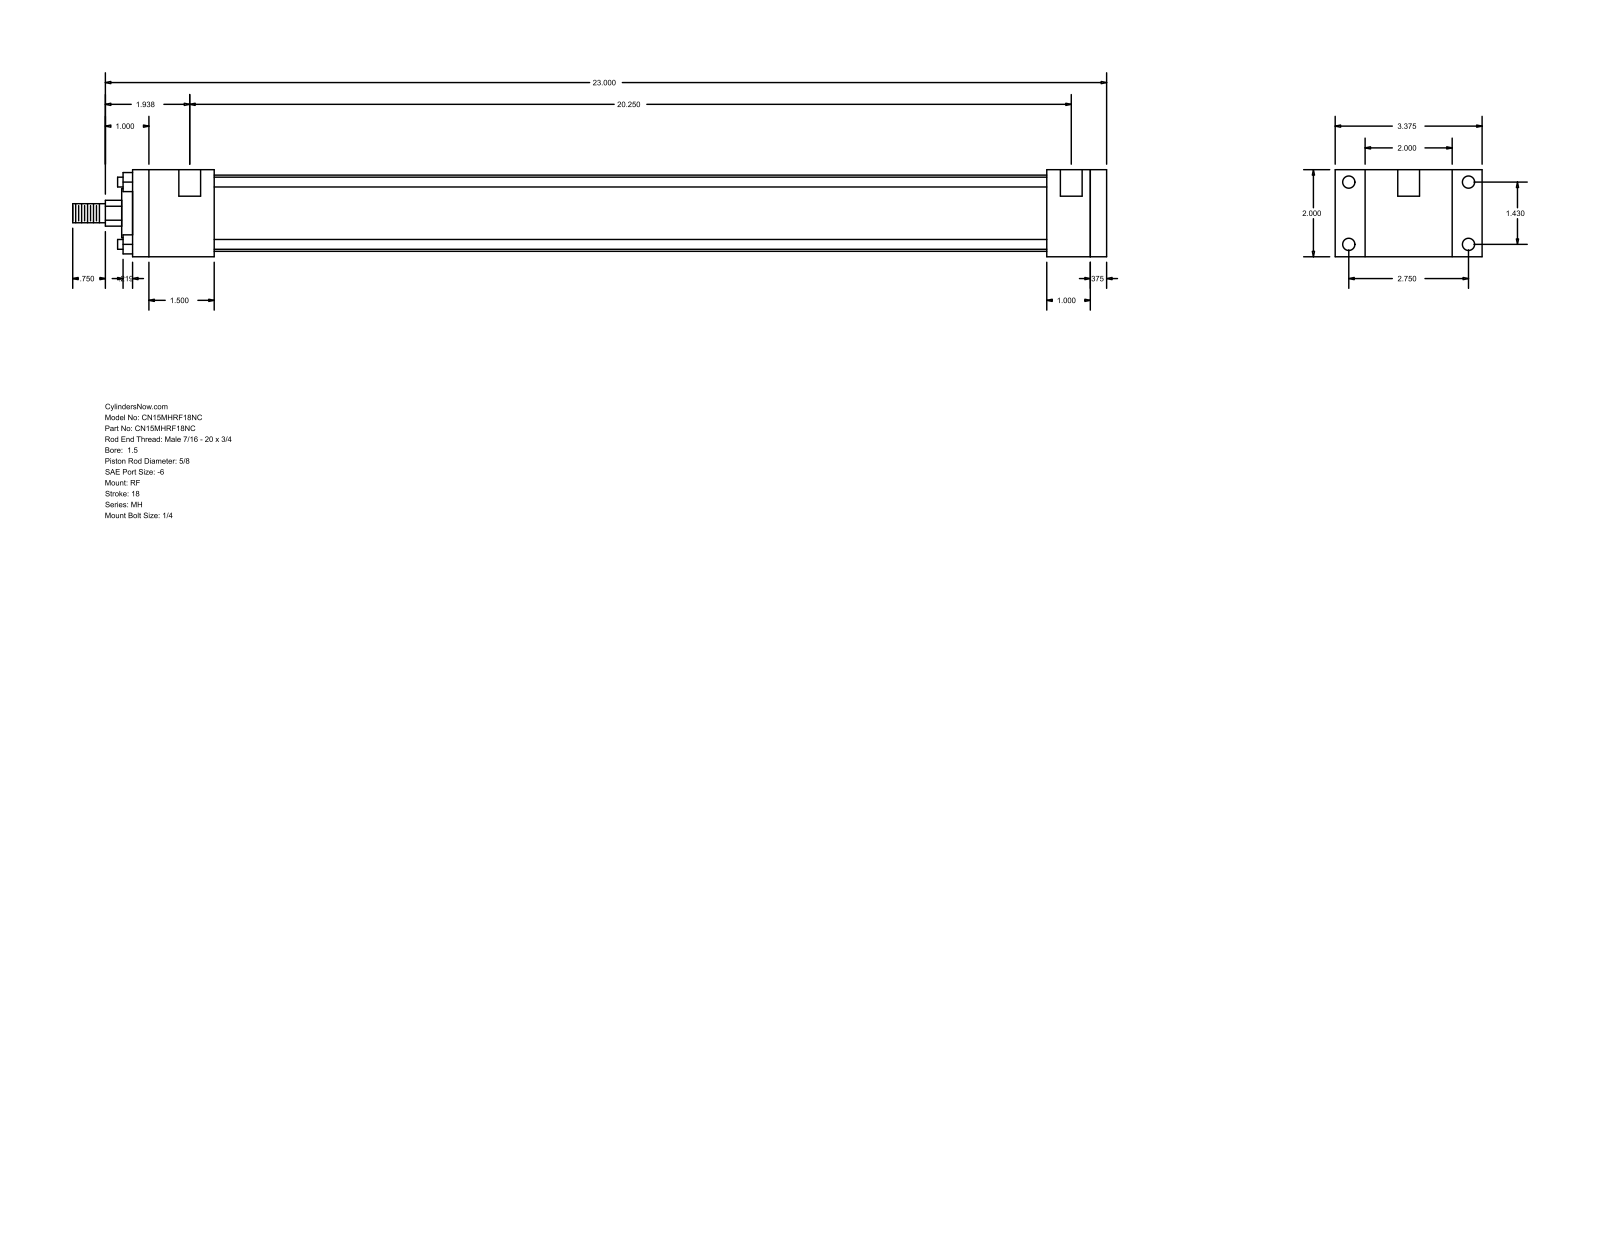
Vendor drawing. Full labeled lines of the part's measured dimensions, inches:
Part name (STEP PRODUCT): MH_RF__0150_0.625
STEP written by: GSSL Pune (CONFIG_CONTROL_DESIGN)
Units: inches
Bodies: 0 solids, 92 faces (64 planar, 28 cylindrical, 0 other)
Overall size (bounding box): 23.75 × 3.375 × 2
Round holes (diameter × count): ⌀0.219 ×4, ⌀0.281 ×4, ⌀0.5 ×2
Round bosses / shafts (diameter × count): ⌀0.225 ×4, ⌀1.75 ×1, ⌀1.125 ×1, ⌀0.625 ×1, ⌀0.437 ×1
Partial cylindrical surfaces — rounded edges, fillets, slot ends (radius × count): R0.297 ×1
Main face-to-face distances: 2, 0.375, 22.375, 22, 1.375, 1, 0.687, 2.687, 21, 1.875
Hole centre spacings: 1.43, 2.75, 3.099, 20.375, 0.125, 20.25
